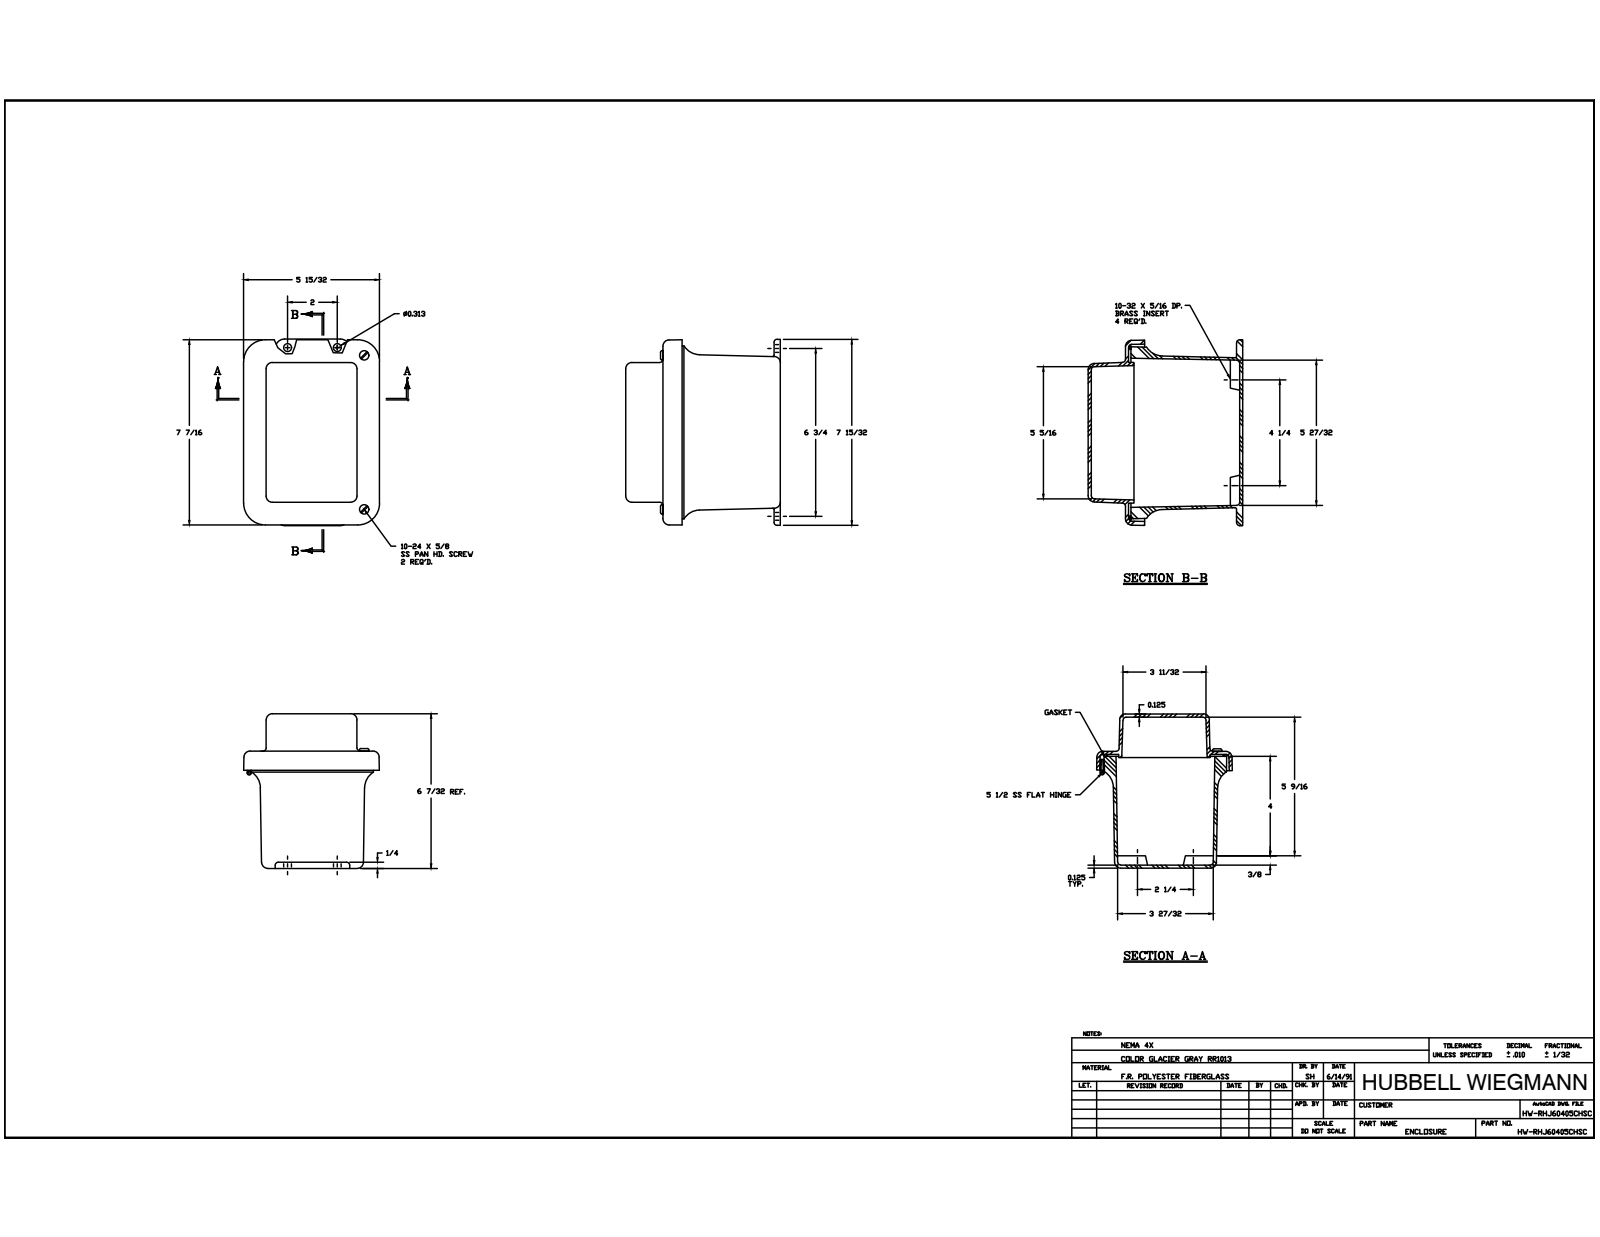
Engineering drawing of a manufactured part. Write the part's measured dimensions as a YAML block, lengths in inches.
part_name: "J604HW_3; RMINS45821P_53; RMINS45821P_54; RMINS45821P_55 (+8 more)"
step_written_by: "Autodesk Inventor 2014 (AUTOMOTIVE_DESIGN)"
units: inches
bodies: {solids: 19, faces: 712, planar: 223, cylindrical: 263, other: 226}
overall_size: [7.474, 6.227, 5.498]
volume: 33.38
surface_area: 446.3
round_holes:
  - {diameter: 0.131, count: 5}
  - {diameter: 0.14, count: 5}
  - {diameter: 0.152, count: 5}
  - {diameter: 0.156, count: 4}
  - {diameter: 0.218, count: 4}
  - {diameter: 0.145, count: 2}
  - {diameter: 0.085, count: 1}
round_bosses_or_shafts:
  - {diameter: 0.27, count: 6}
  - {diameter: 0.25, count: 5}
  - {diameter: 0.125, count: 5}
  - {diameter: 0.19, count: 2}
  - {diameter: 0.156, count: 2}
  - {diameter: 0.155, count: 1}
partial_cylinders:
  - {radius: 0.031, count: 20}
  - {radius: 0.125, count: 20}
  - {radius: 0.25, count: 12}
  - {radius: 0.2, count: 4}
  - {radius: 0.309, count: 4}
  - {radius: 0.313, count: 4}
  - {radius: 0.375, count: 4}
  - {radius: 0.75, count: 4}
face_to_face_distances: [0.125, 4.602, 6.102, 1.5, 6.227, 1.625, 4.477, 5.977, 0.774, 4.727]
hole_center_spacings: [2.5, 3.339, 0.5, 1.341, 2, 2.25, 4, 4.156]
